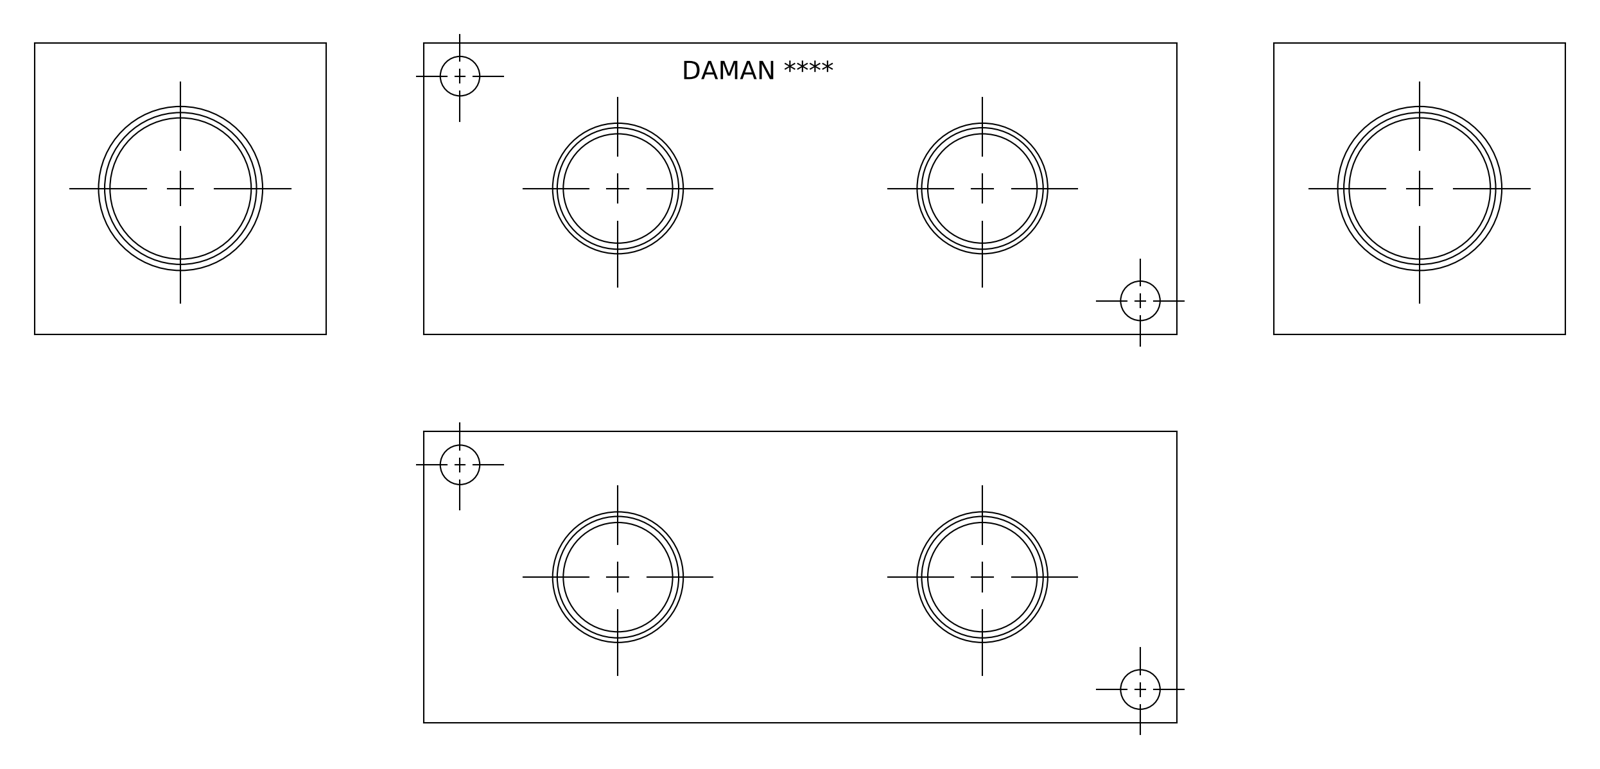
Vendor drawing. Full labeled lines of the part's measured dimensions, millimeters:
Part name (STEP PRODUCT): Part_AH0900216P.C13745R0_3D
STEP written by: Autodesk Inventor 2019 (AUTOMOTIVE_DESIGN)
Units: millimetres
Bodies: 1 solid, 349 faces (221 planar, 20 cylindrical, 108 other)
Overall size (bounding box): 196.85 × 76.2 × 76.2
Volume: 976 766 mm³ · Surface area: 94 916 mm²
Round holes (diameter × count): ⌀10.31 ×4, ⌀28.57 ×4, ⌀33.71 ×4, ⌀36.91 ×1, ⌀42.47 ×1
Main face-to-face distances: 76.2, 196.85, 19, 57.2, 19.51, 177.34, 157.83, 75.2, 18, 1
Hole centre spacings: 50.65, 139.64, 95.25, 187.24
